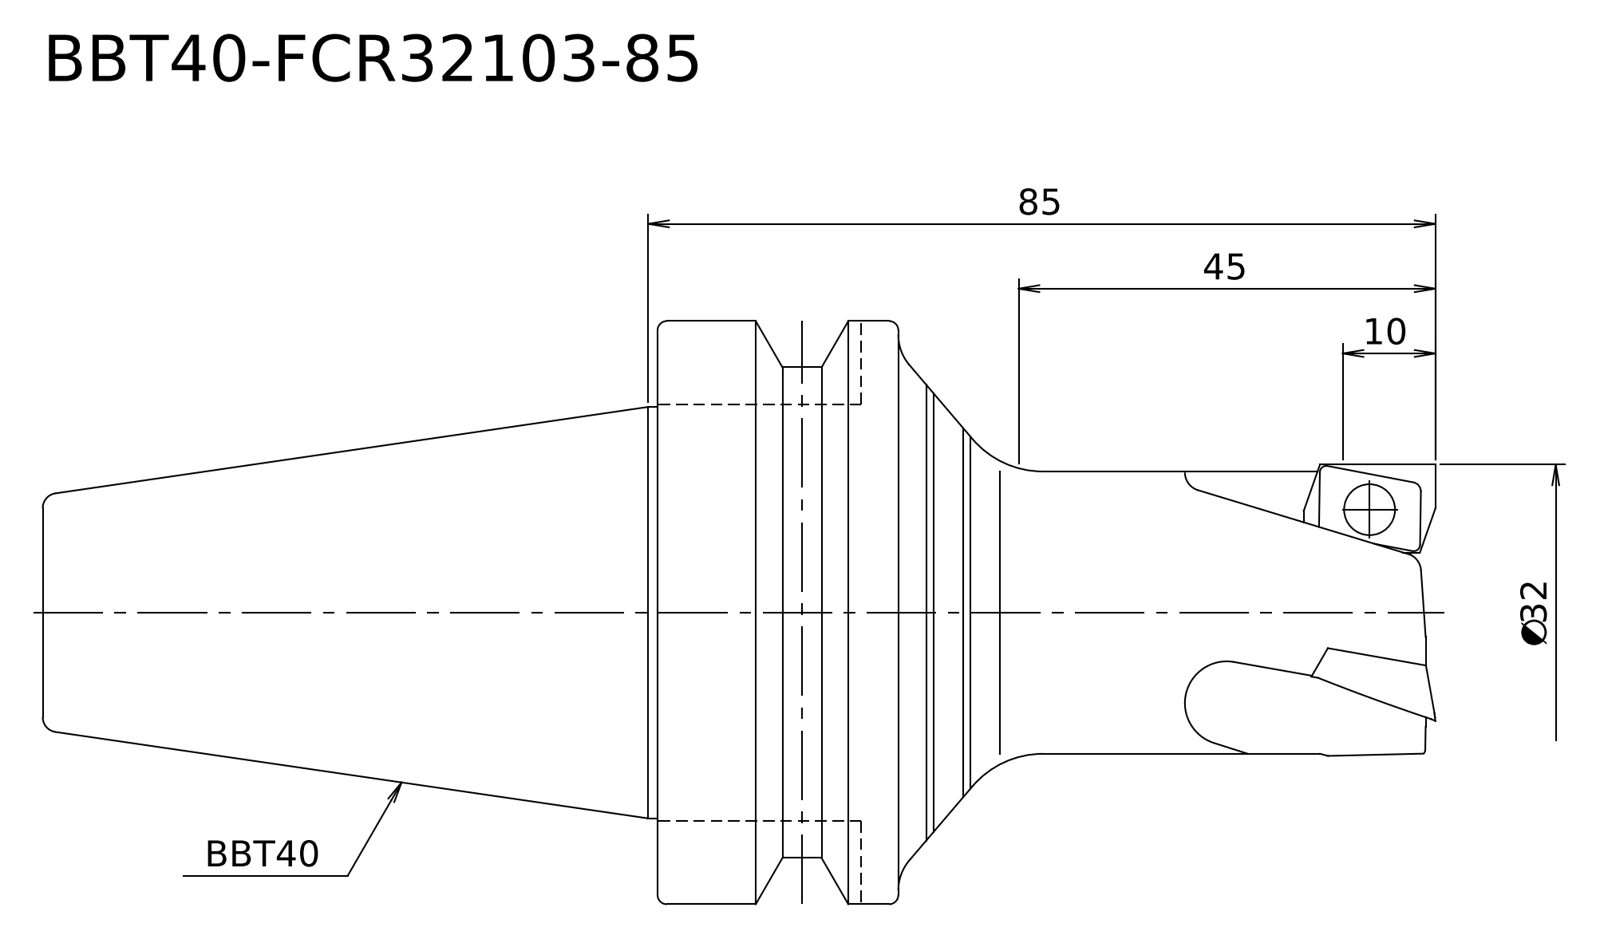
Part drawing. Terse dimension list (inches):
written by: Kubotek KeyCreator V8.5.1 (14335) (CONFIG_CONTROL_DESIGN)
unit: in
bodies: 1 solid, 17 faces (4 planar, 6 cylindrical, 7 other)
size: 5.921 × 2.48 × 2.48
volume: 11.79 in³; area: 36.68 in²
bosses: 1× ⌀2.48, 1× ⌀2.087, 1× ⌀1.75, 1× ⌀1.26, 1× ⌀1.201
face distances: 3.307, 5.921, 2.614, 2.283, 1.024, 3.638
